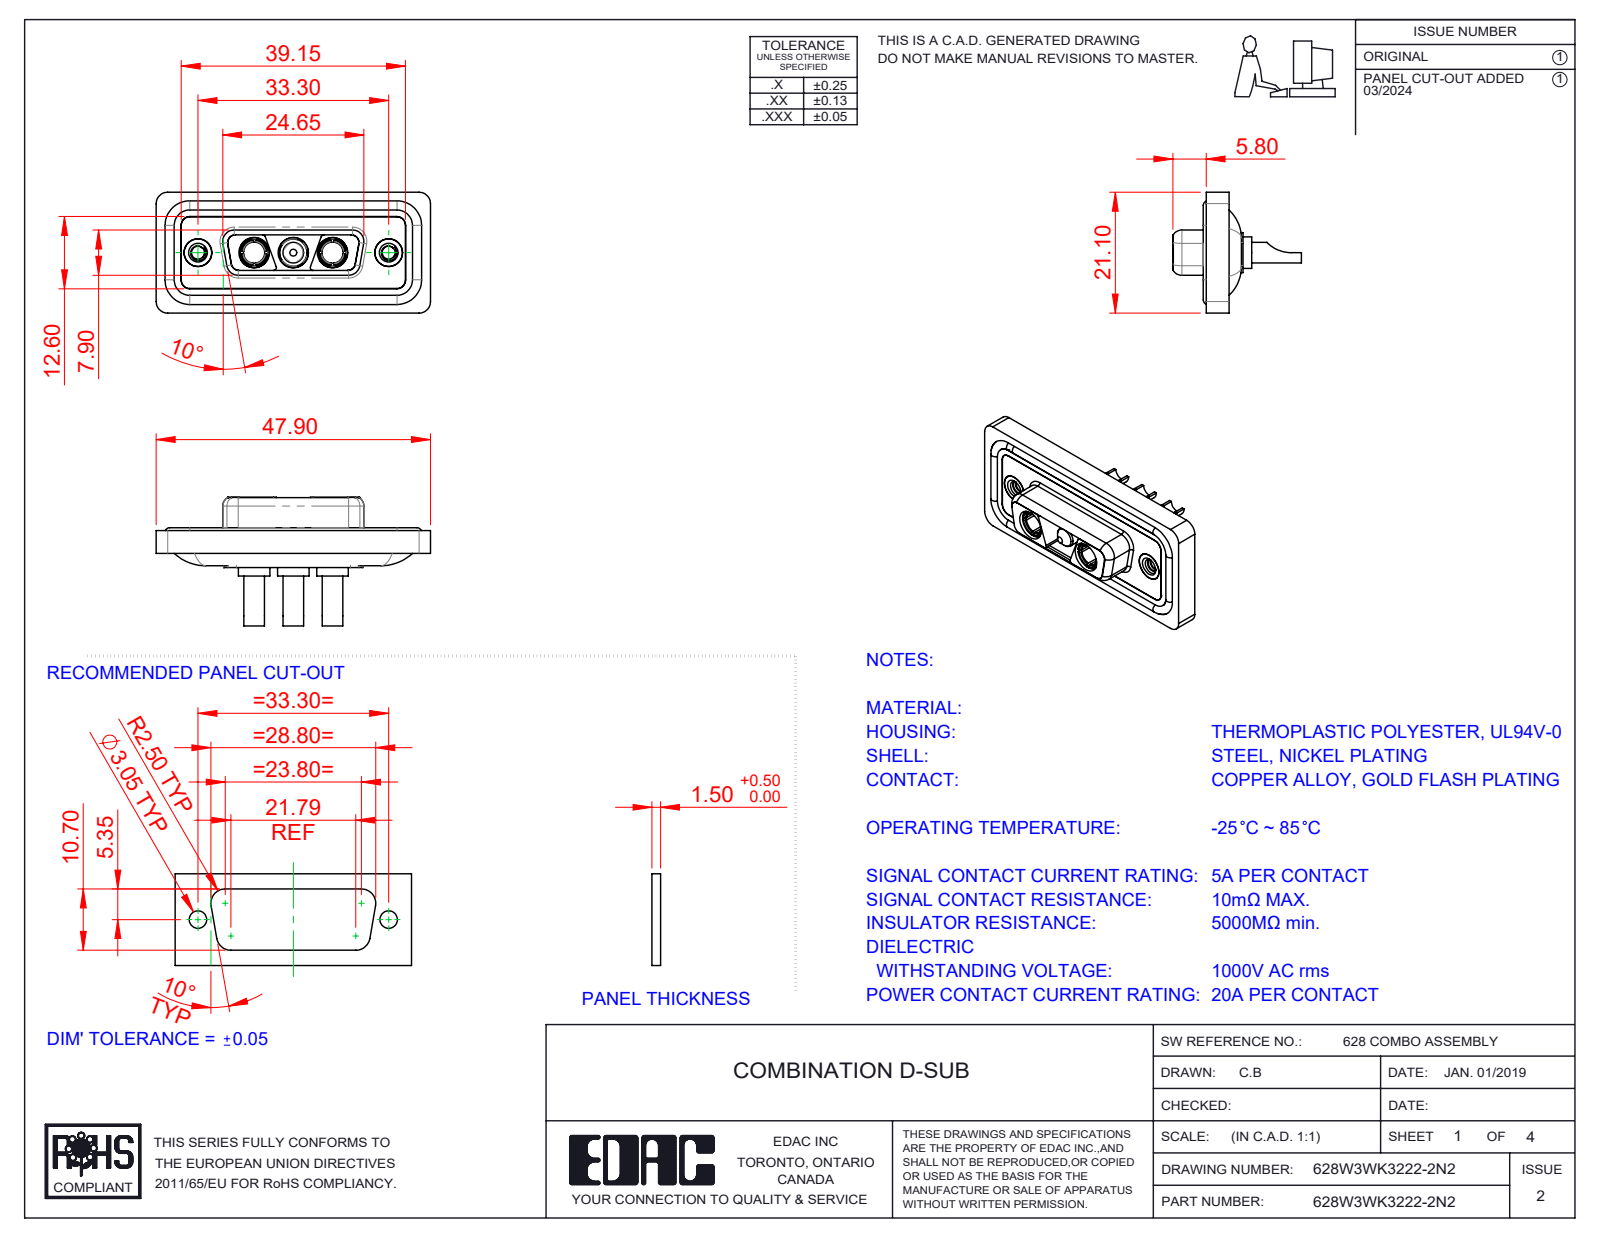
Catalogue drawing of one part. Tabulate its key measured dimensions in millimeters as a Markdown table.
| quantity | value |
| --- | --- |
| part name | 628Combo Waterproof Housing_15 Contacts; 628Combo Shell Rear_15 Contacts; Power Pin_20A SC; Power Socket_20A SC (+4 more) |
| STEP written by | SolidWorks 2023 (CONFIG_CONTROL_DESIGN) |
| units | millimeters |
| bodies | 13 solids, 602 faces (187 planar, 267 cylindrical, 148 other) |
| overall size | 47.9 × 22.45 × 21.1 |
| volume | 5 916 mm³ |
| surface area | 9 752 mm² |
| round holes (diameter × count) | 4.85 × 5, 2.7 × 3, 5.3 × 3, 2.26 × 2, 3.7 × 2, 4 × 2, 4.05 × 2, 5 × 2 |
| round bosses / shafts (diameter × count) | 1.6 × 4, 5.5 × 3, 5.2 × 3, 4.75 × 3, 3.75 × 3, 3.6 × 3, 4.96 × 2, 4.95 × 2 |
| partial cylindrical surfaces (radius × count) | 1.5 × 22, 2 × 20, 1.35 × 12, 0.5 × 8, 1.6 × 8, 0.25 × 4, 0.6 × 4, 0.65 × 4 |
| main face-to-face distances | 0.4, 1.6, 0.5, 1.8, 1.1, 2.9, 5.65, 7.05, 5.35, 1.5 |
| hole center spacings | 6.85, 9.8, 16.65, 23.5, 13.7, 33.3 |
